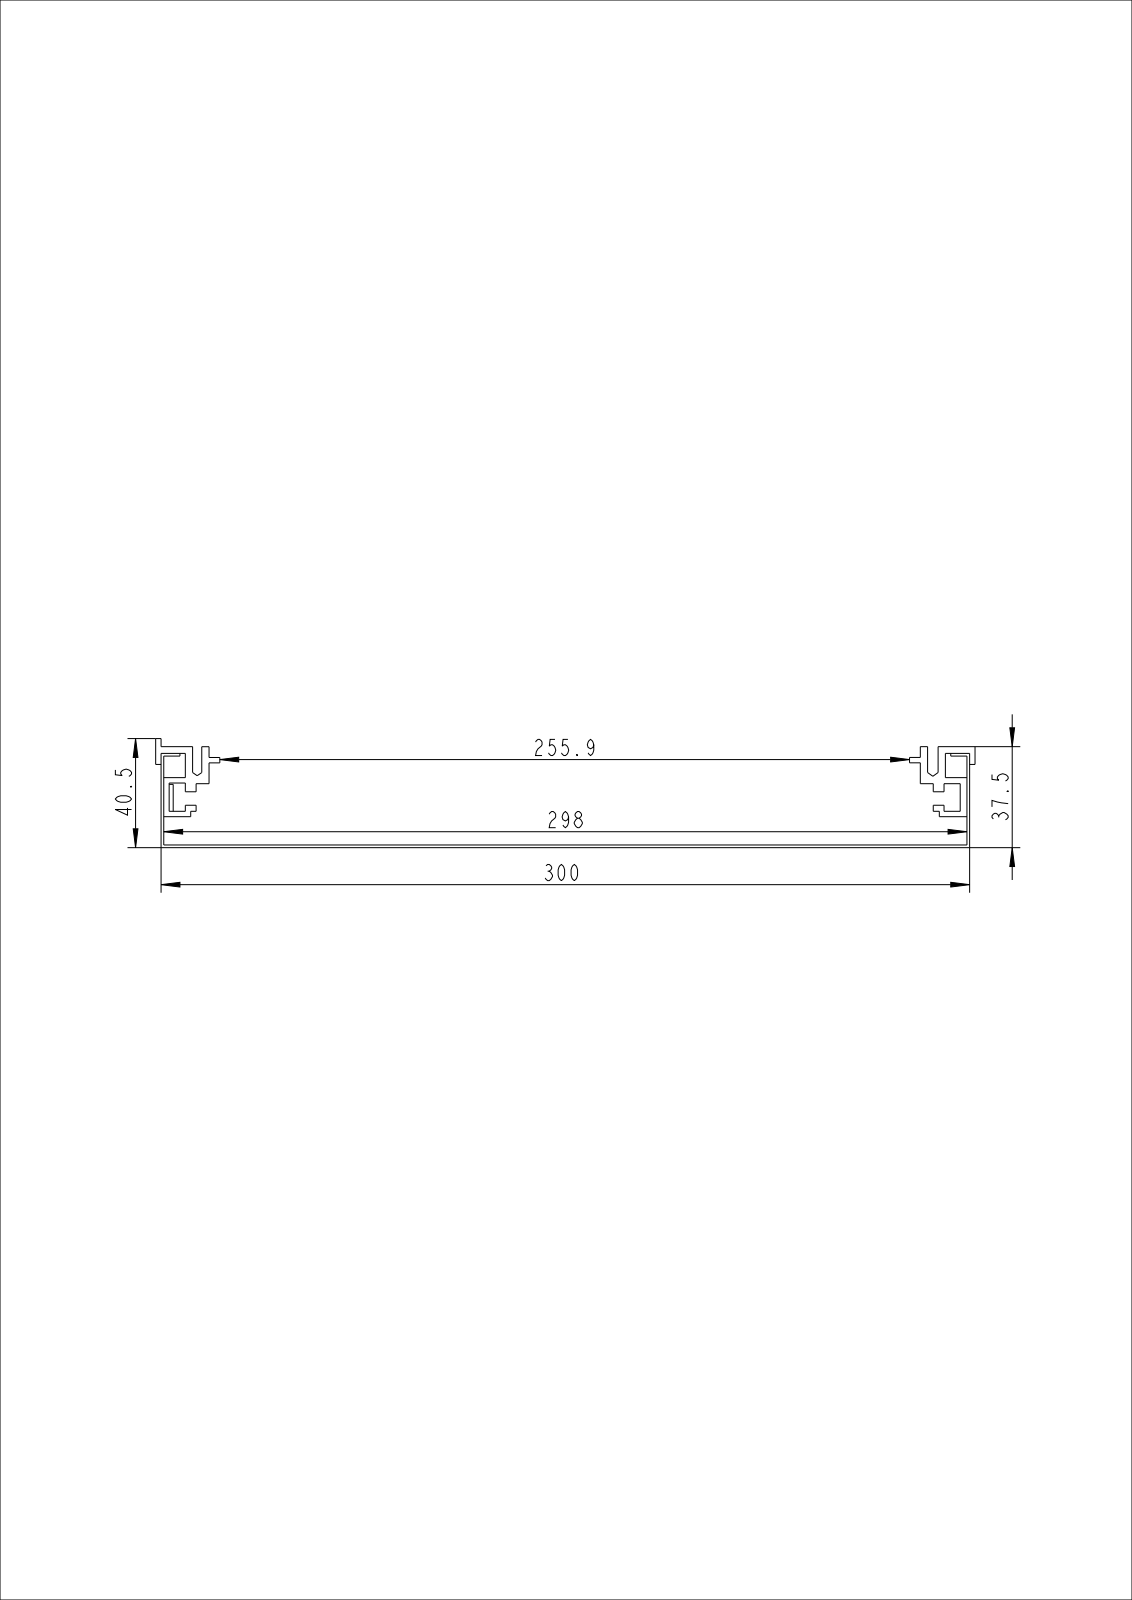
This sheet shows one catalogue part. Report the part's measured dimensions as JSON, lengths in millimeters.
{"part_name": "AKU3000401_WANNE_3; AKU_SEITENPROFIL_APA_K24_6; ZES_VK180_KUN_3; AKU_SEITENPROFIL_APA_O01_4 (+2 more)", "step_written_by": "CREO PARAMETRIC BY PTC INC, 2022281 (AUTOMOTIVE_DESIGN)", "units": "millimeters", "bodies": {"solids": 9, "faces": 265, "planar": 253, "cylindrical": 12, "other": 0}, "overall_size": [2450, 304, 40.5], "volume_mm3": 1557000, "surface_area_mm2": 2374000, "round_holes": [[5.5, 4], [4.2, 2]], "face_to_face_distances": [1, 299, 2, 34, 298, 300, 8, 3, 9, 12.5], "hole_center_spacings": [9.25, 66.5, 18.5, 57.25, 75.75, 48, 85]}
